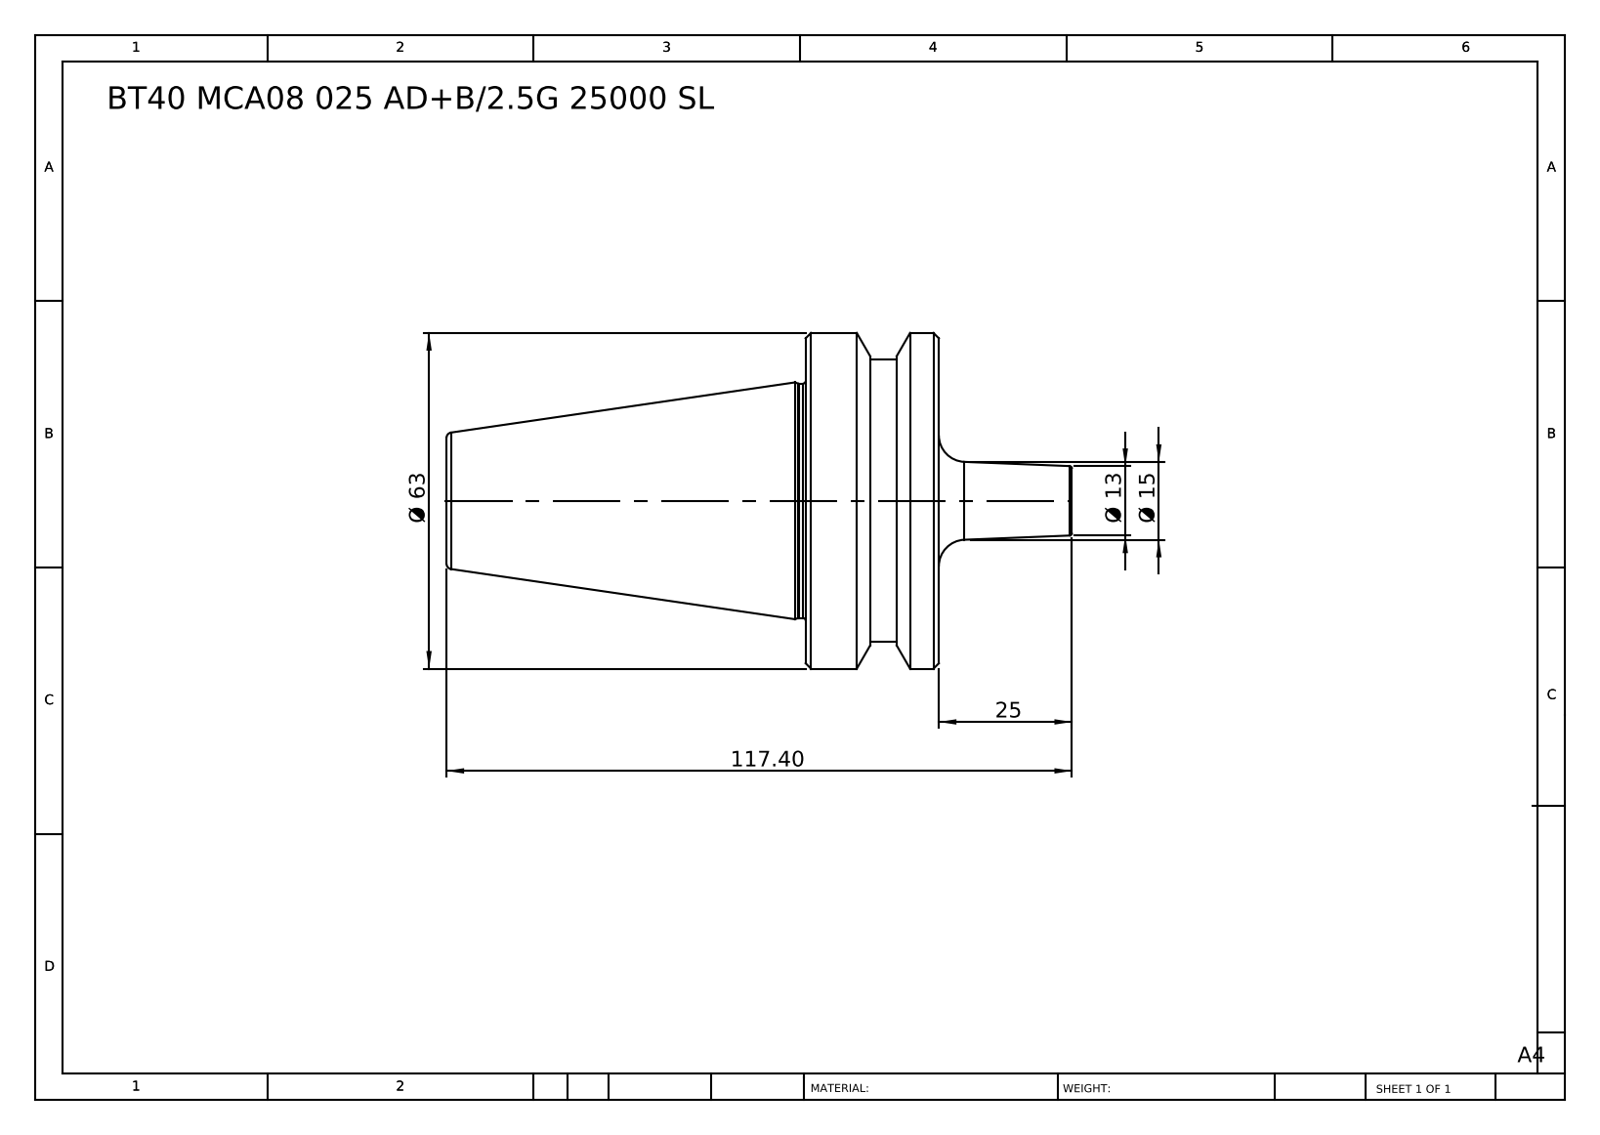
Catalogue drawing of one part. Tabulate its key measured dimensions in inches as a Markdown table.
| quantity | value |
| --- | --- |
| part name | BT40 MCA08 025 AD+B-2.5G 25000 SL |
| STEP written by | SolidWorks 2014 (CONFIG_CONTROL_DESIGN) |
| units | inches |
| bodies | 1 solid, 38 faces (6 planar, 8 cylindrical, 24 other) |
| overall size | 4.622 × 2.48 × 2.48 |
| volume | 8.694 in³ |
| surface area | 29.92 in² |
| round bosses / shafts (diameter × count) | 2.48 × 1, 2.087 × 1, 1.732 × 1 |
| main face-to-face distances | 0.984, 3.638, 2.654, 1.969, 4.622, 1.492, 0.508, 0.476, 3.13, 1.295 |
